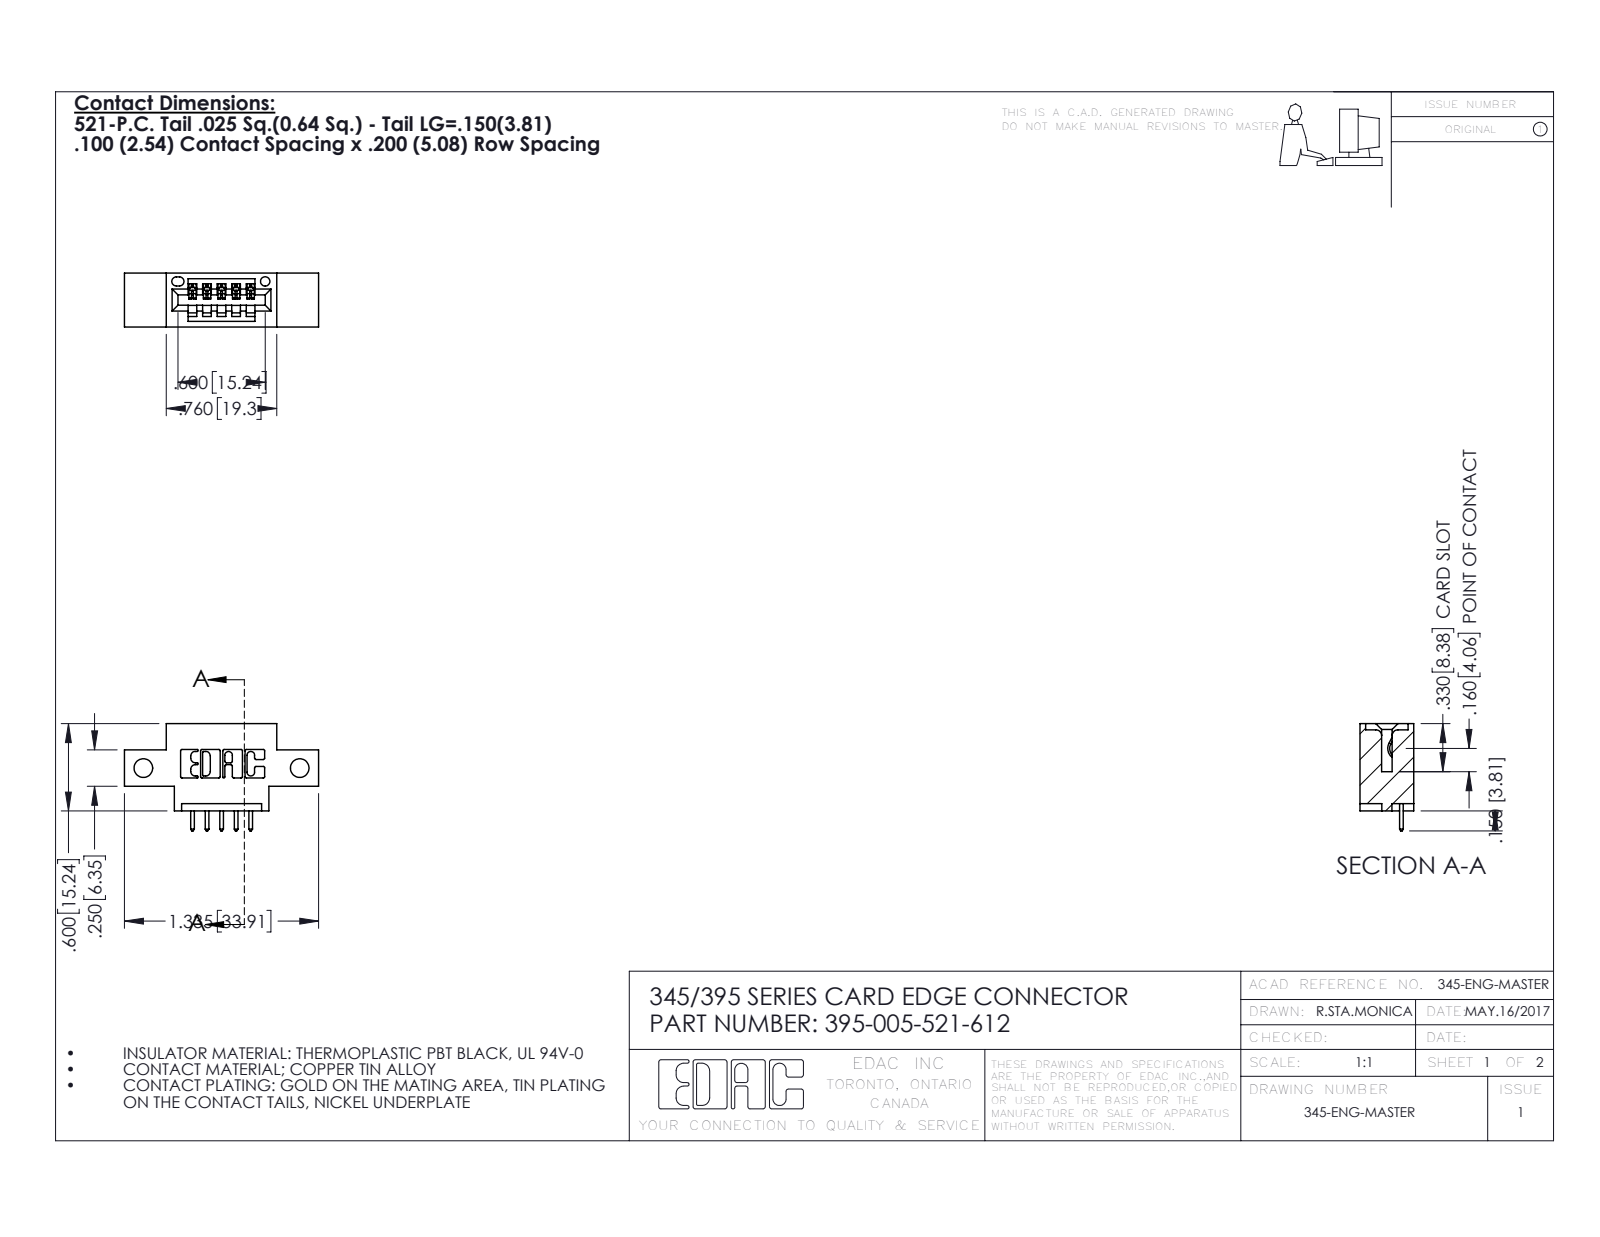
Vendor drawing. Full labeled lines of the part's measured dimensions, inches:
Part name (STEP PRODUCT): 345 Part_0.170 Offset - Side Mount; 345-292-001_345-293-121; 395-005-521-612
STEP written by: SolidWorks 2016 (CONFIG_CONTROL_DESIGN)
Units: inches
Bodies: 6 solids, 420 faces (284 planar, 136 cylindrical, 0 other)
Overall size (bounding box): 1.335 × 0.737 × 0.37
Volume: 0.165 in³ · Surface area: 4.677 in²
Round holes (diameter × count): ⌀0.128 ×2, ⌀0.064 ×1
Partial cylindrical surfaces — rounded edges, fillets, slot ends (radius × count): R0.01 ×22, R0.006 ×10, R0.01 ×10, R0.007 ×6, R0.031 ×6, R0.026 ×3, R0.031 ×2, R0.04 ×2
Main face-to-face distances: 0.37, 0.2, 0.1, 0.298, 0.072, 0.25, 0.025, 0.098, 0.272, 0.06
Hole centre spacings: 1.075
